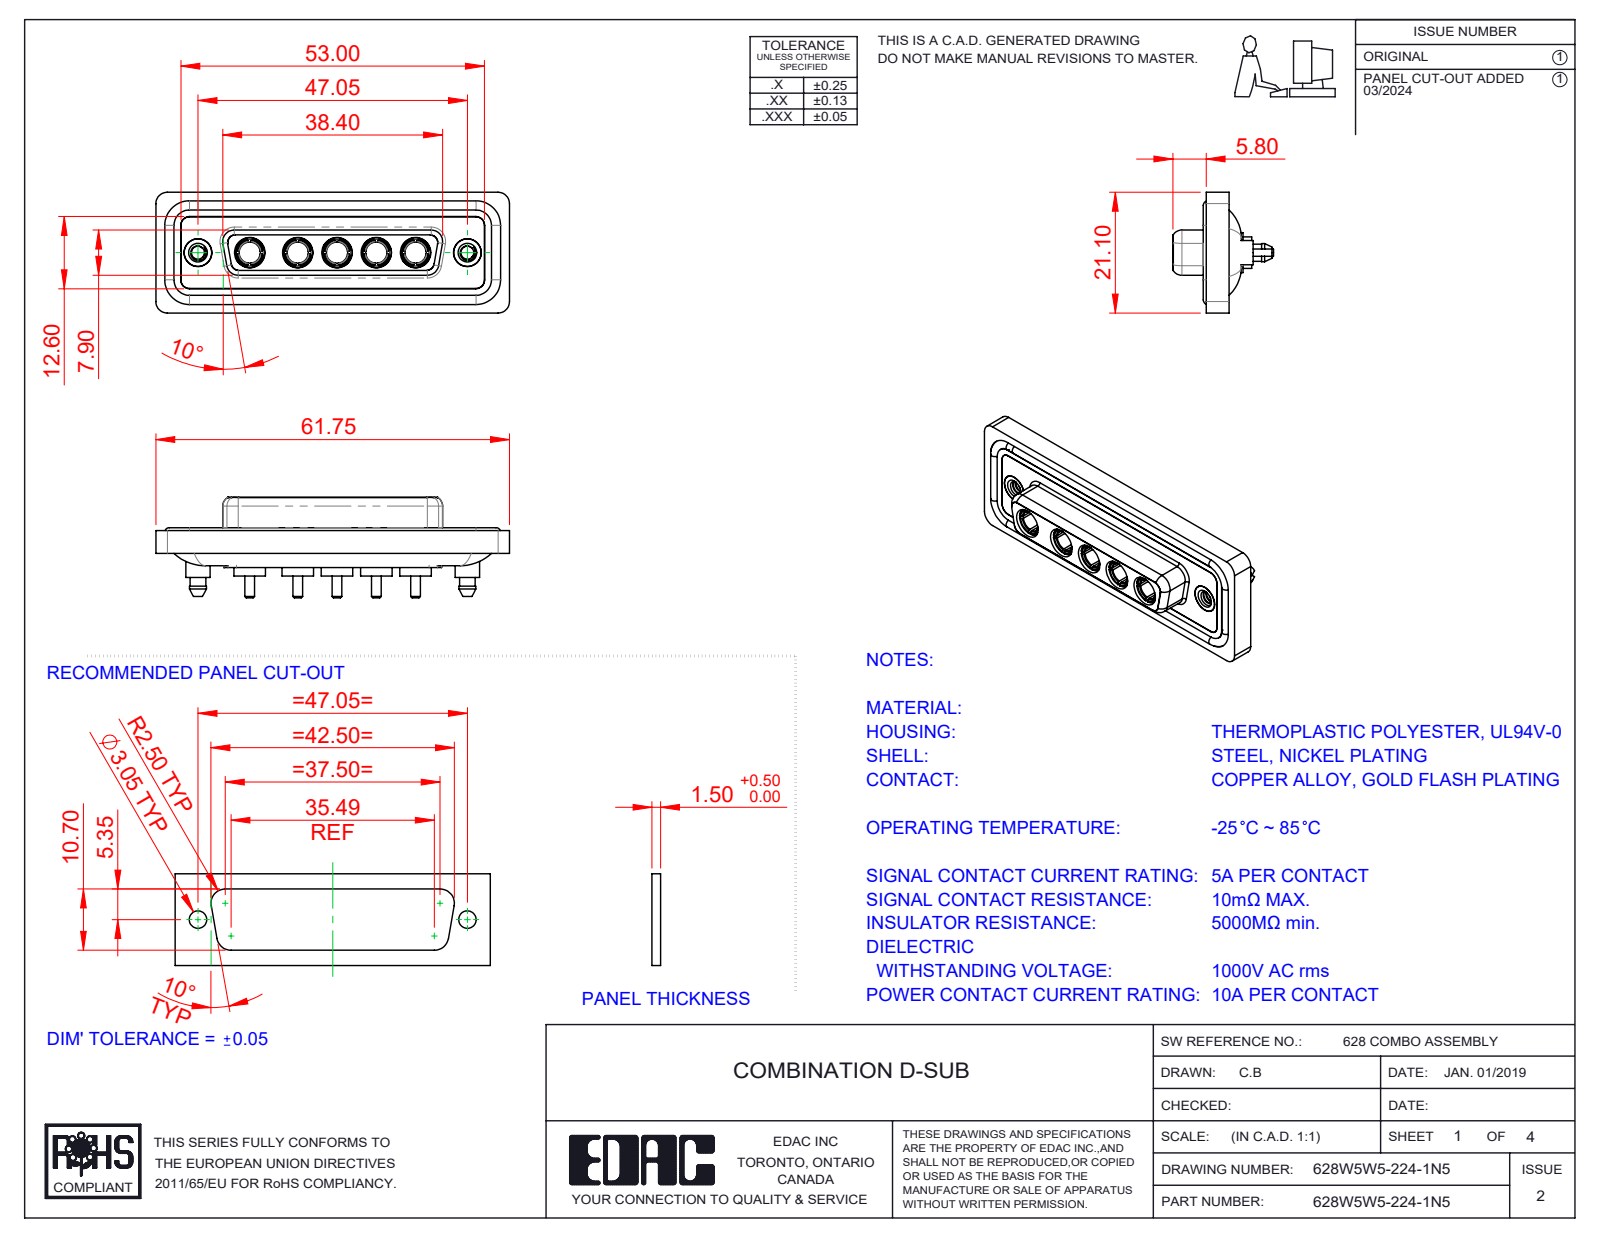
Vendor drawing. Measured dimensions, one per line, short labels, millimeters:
name: 628Combo Housing_5W5; Power Socket_10A S; 628W5W5-224-1N5; 628Combo Waterproof Housing_25 Contacts (+3 more)
written by: SolidWorks 2023 (CONFIG_CONTROL_DESIGN)
unit: mm
bodies: 17 solids, 806 faces (266 planar, 335 cylindrical, 205 other)
size: 61.75 × 21.1 × 17.55
volume: 8 233 mm³; area: 13 685 mm²
holes: 7× ⌀4.85, 5× ⌀3.7, 5× ⌀5.3, 2× ⌀2.26, 2× ⌀4, 2× ⌀4.05, 2× ⌀5
bosses: 5× ⌀5.5, 5× ⌀5.2, 5× ⌀4.96, 5× ⌀4.75, 5× ⌀3.75, 5× ⌀1.7, 4× ⌀1.6, 2× ⌀5.4
rounds: 24× R1.5, 18× R2, 10× R1.6, 8× R1.35, 5× R2.1, 4× R0.25, 4× R0.5, 4× R0.6
face distances: 0.4, 1.8, 7.45, 5.65, 0.5, 7.05, 6.6, 1.6, 1.1, 1.5
hole spacings: 6.86, 9.04, 13.72, 38.01, 8.39, 15.25, 15.9, 17.43
